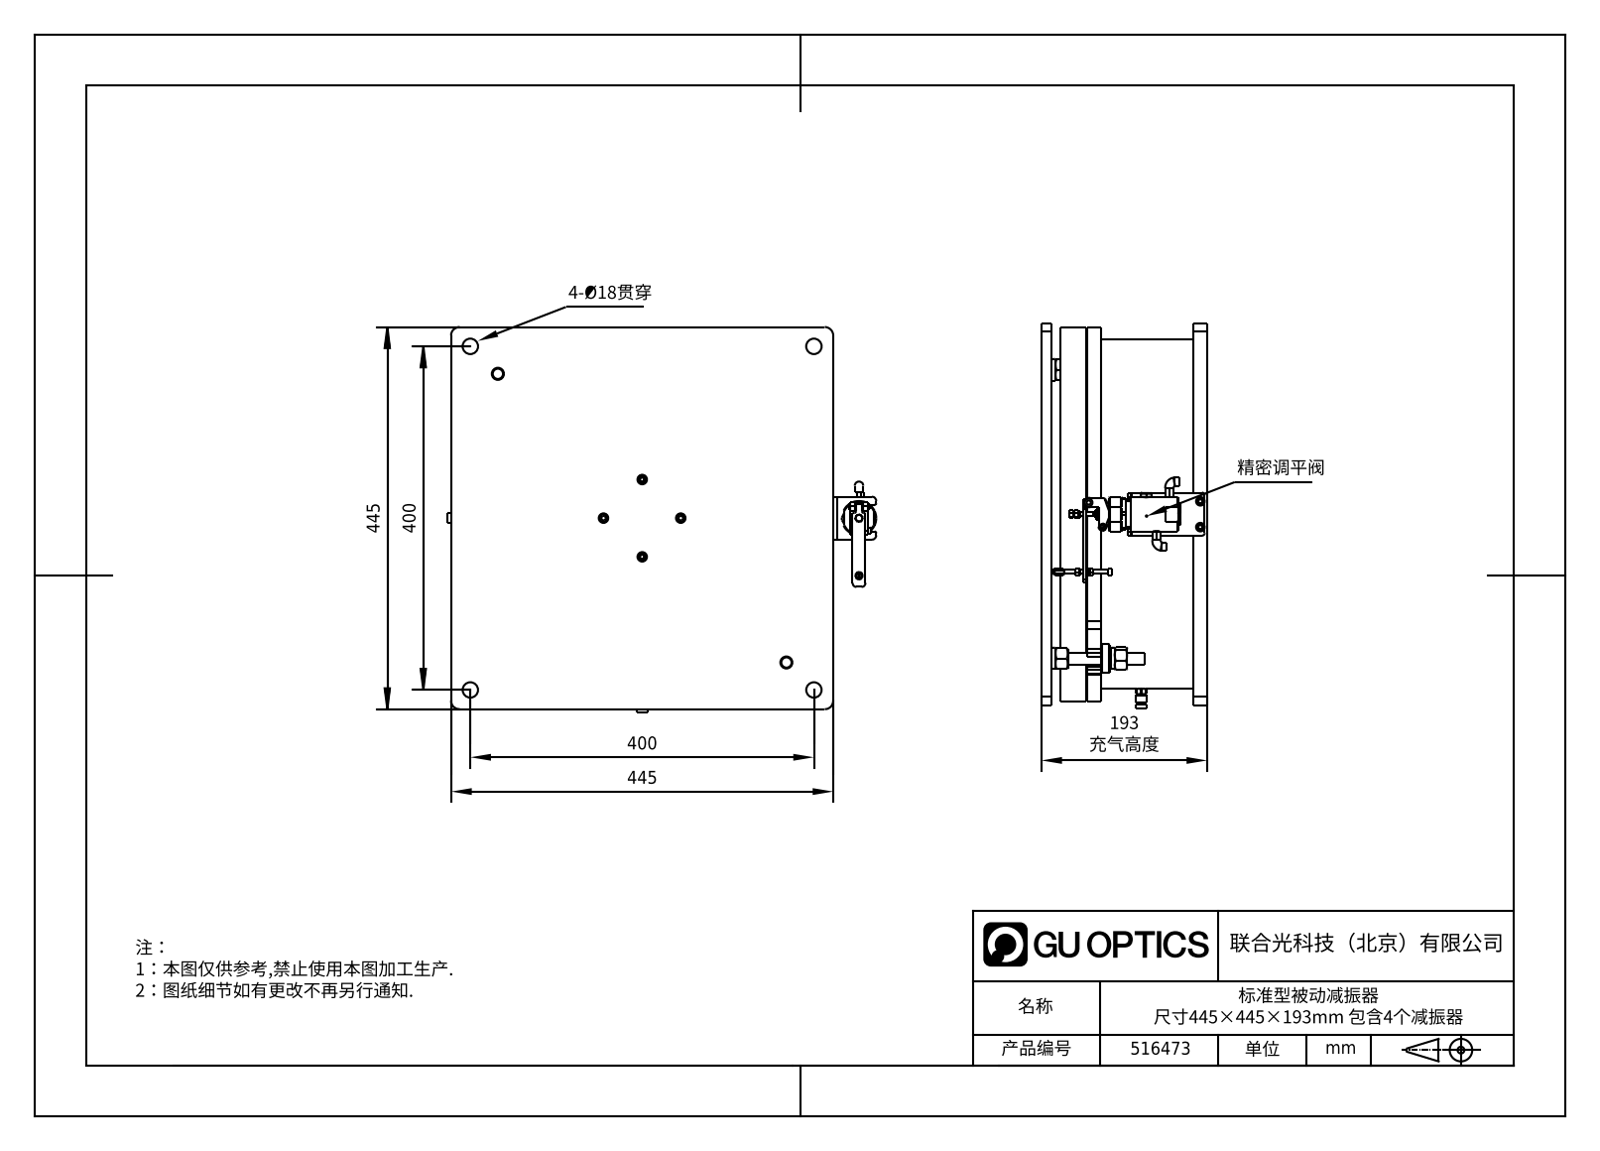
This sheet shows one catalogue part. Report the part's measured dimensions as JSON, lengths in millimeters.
{"part_name": "516473", "step_written_by": "SolidWorks 2020 (AUTOMOTIVE_DESIGN)", "units": "millimeters", "bodies": {"solids": 0, "faces": 432, "planar": 242, "cylindrical": 134, "other": 56}, "overall_size": [499.2, 449.2, 193], "round_holes": [[9.7, 3], [18, 2], [5, 1], [13, 1], [40, 1], [435, 1]], "round_bosses_or_shafts": [[11, 5], [18, 4], [12.7, 3], [12.6, 3], [12, 3], [10.4, 3], [10, 3], [8.45, 3]], "partial_cylinders_radius": [[5, 10], [10, 8], [2, 3], [7, 3], [0.3, 2], [3, 2], [11, 2], [4.5, 1]], "face_to_face_distances": [16, 181, 193, 177, 165, 12, 124, 69, 108, 57], "hole_center_spacings": [237.59, 37, 188.05, 236.7, 252.5, 452.82, 475.18]}
